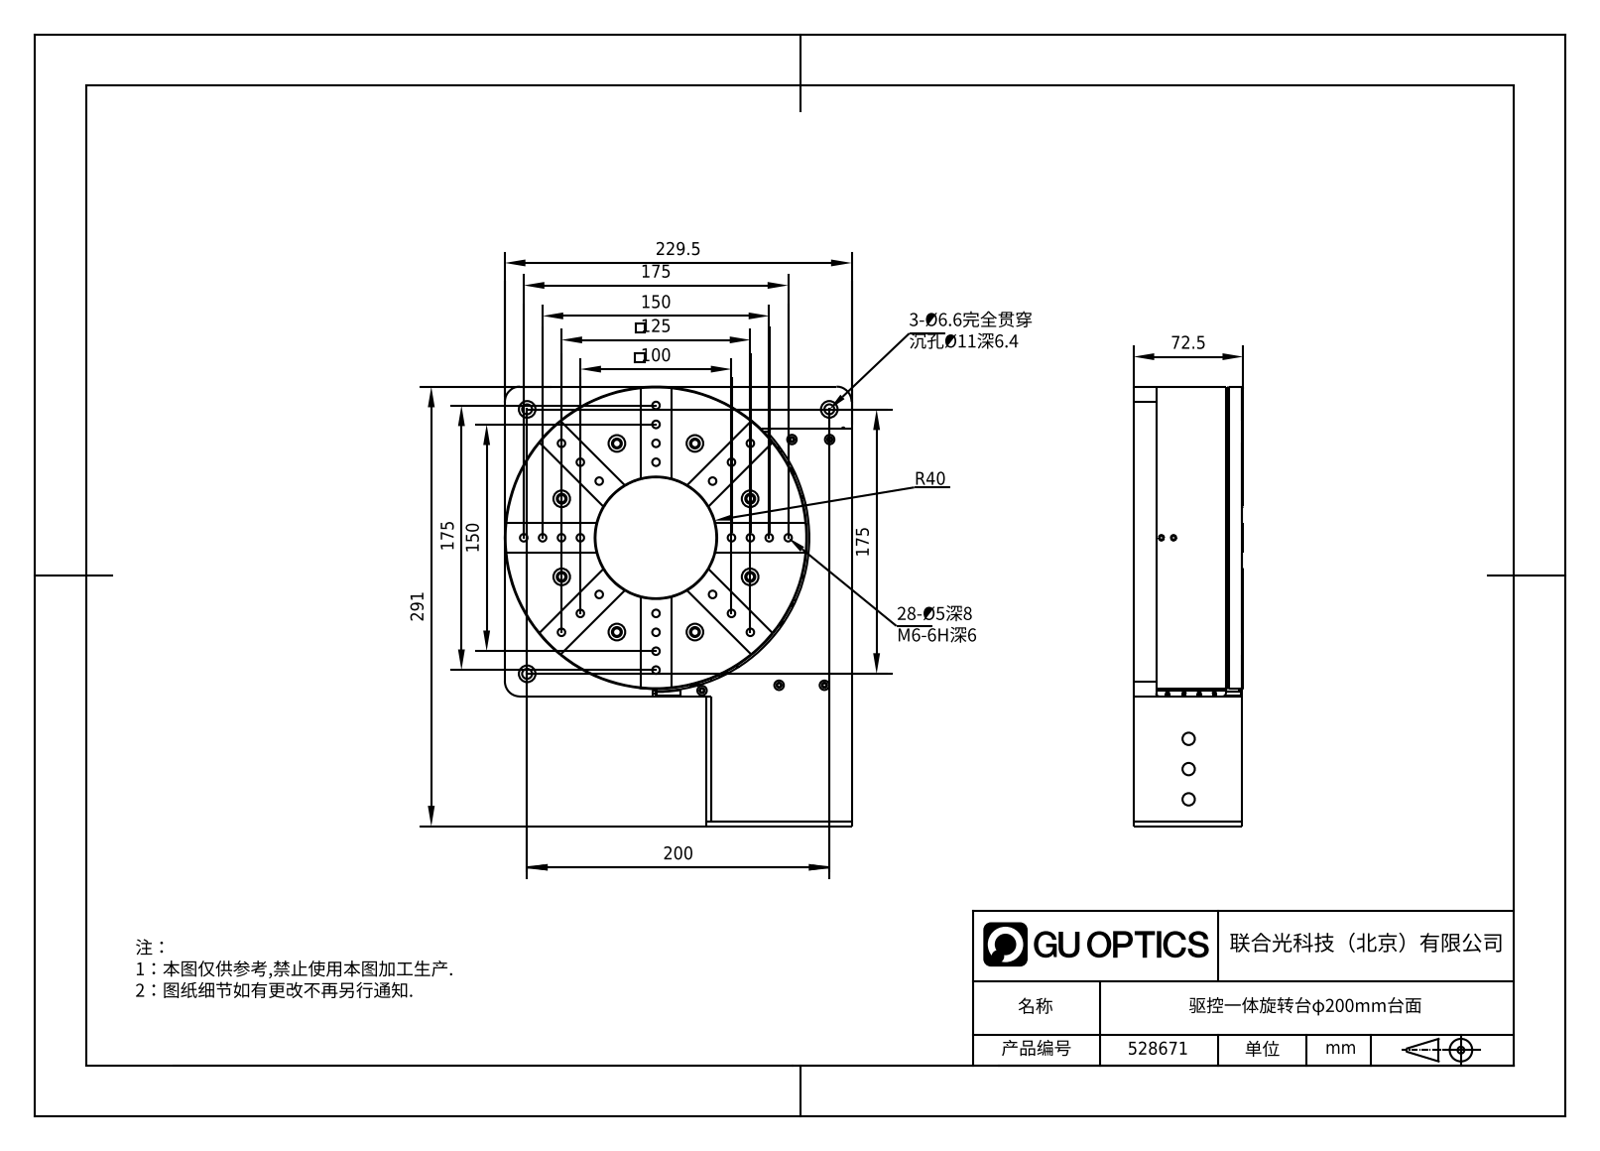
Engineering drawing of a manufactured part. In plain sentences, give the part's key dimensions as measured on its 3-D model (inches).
The part is named "528671". Its 3-D file was written by "SolidWorks 2020 (CONFIG_CONTROL_DESIGN)". It is 26 solids with 2959 faces: 470 planar, 2062 cylindrical and 427 other. Overall it measures 11.457 by 9.035 by 2.854 inches. Its volume is 142.9 cubic inches and its surface area 925.7 square inches. Round holes: 49 of diameter 0.197, 26 of diameter 0.217, 23 of diameter 0.098, 17 of diameter 0.13, 17 of diameter 0.394, 16 of diameter 0.165, 16 of diameter 0.26, 16 of diameter 0.433, 11 of diameter 0.134, 10 of diameter 0.177, 10 of diameter 0.315, 10 of diameter 0.374. Round bosses or shafts: 1 of diameter 7.874, 1 of diameter 6.89, 1 of diameter 6.496, 1 of diameter 6.437, 1 of diameter 4.646, 1 of diameter 1.504, 1 of diameter 0.984, 1 of diameter 0.614. Partial cylindrical surfaces (rounded edges, fillets, slot ends): 12 of radius 0.039, 8 of radius 0.13, 8 of radius 0.236, 6 of radius 0.079, 4 of radius 0.043, 3 of radius 0.394, 2 of radius 0.118, 1 of radius 0.197. The main face-to-face distances are 2.224, 0.512, 0.02, 0.079, 0.098, 0.591, 2.244, 2.323, 1.713, 1.319. The hole center spacings are 3.48, 4.058, 0.696, 1.18, 1.909, 2.245, 4.456, 2.461.
